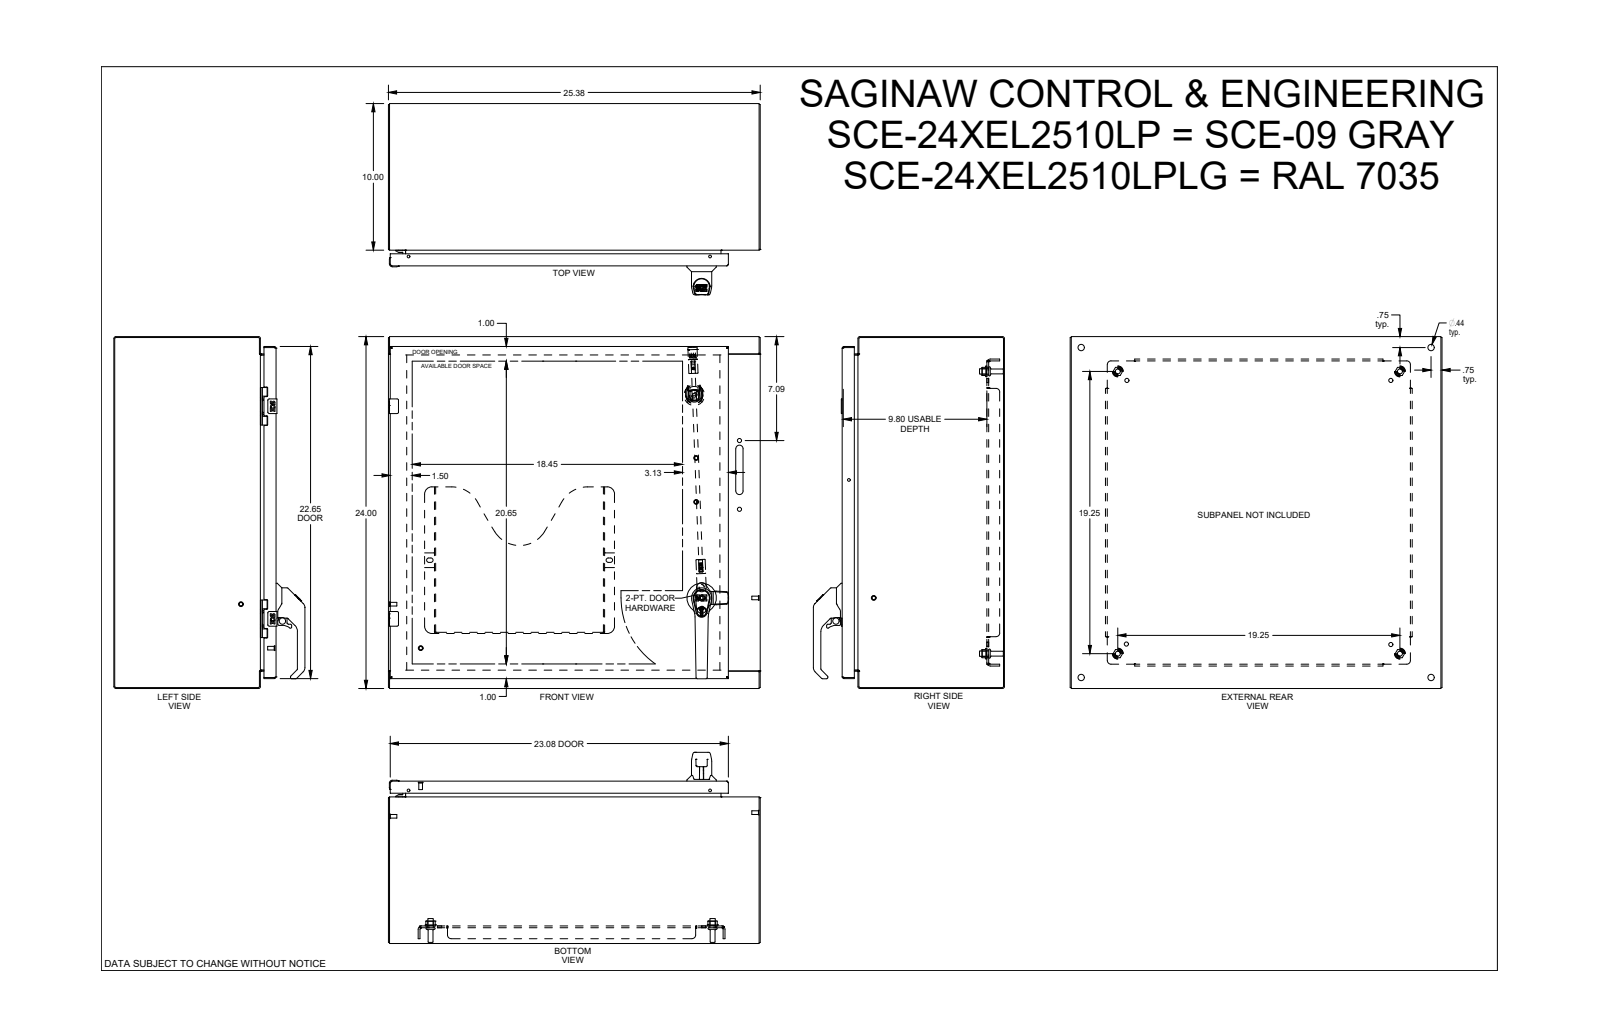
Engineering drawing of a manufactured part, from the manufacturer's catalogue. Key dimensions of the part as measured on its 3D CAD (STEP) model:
Part name (STEP PRODUCT): SCE-24XEL2510LP
STEP written by: SolidWorks 2019 (CONFIG_CONTROL_DESIGN)
Units: inches
Bodies: 0 solids, 4640 faces (1749 planar, 1224 cylindrical, 1667 other)
Overall size (bounding box): 25.375 × 24 × 13.041
Round holes (diameter × count): ⌀0.281 ×6, ⌀0.266 ×5, ⌀0.172 ×4, ⌀0.205 ×4, ⌀0.244 ×4, ⌀0.367 ×4, ⌀0.375 ×4, ⌀0.437 ×4, ⌀0.5 ×4, ⌀0.188 ×3, ⌀0.25 ×3, ⌀0.25 ×3
Round bosses / shafts (diameter × count): ⌀0.248 ×8, ⌀0.17 ×6, ⌀0.366 ×4, ⌀0.332 ×4, ⌀0.25 ×4, ⌀0.24 ×4, ⌀0.563 ×3, ⌀0.196 ×3
Partial cylindrical surfaces — rounded edges, fillets, slot ends (radius × count): R0.03 ×71, R0.015 ×54, R0.02 ×43, R0.02 ×36, R0.01 ×32, R0.039 ×30, R0.005 ×26, R0.04 ×25
Main face-to-face distances: 0.075, 0.075, 10.998, 10.923, 11.073, 10.998, 1.2, 9.873, 23.925, 25.3
Hole centre spacings: 14.5, 0.985, 0.02, 0.493, 0.494, 4.493, 0.472, 0.725
